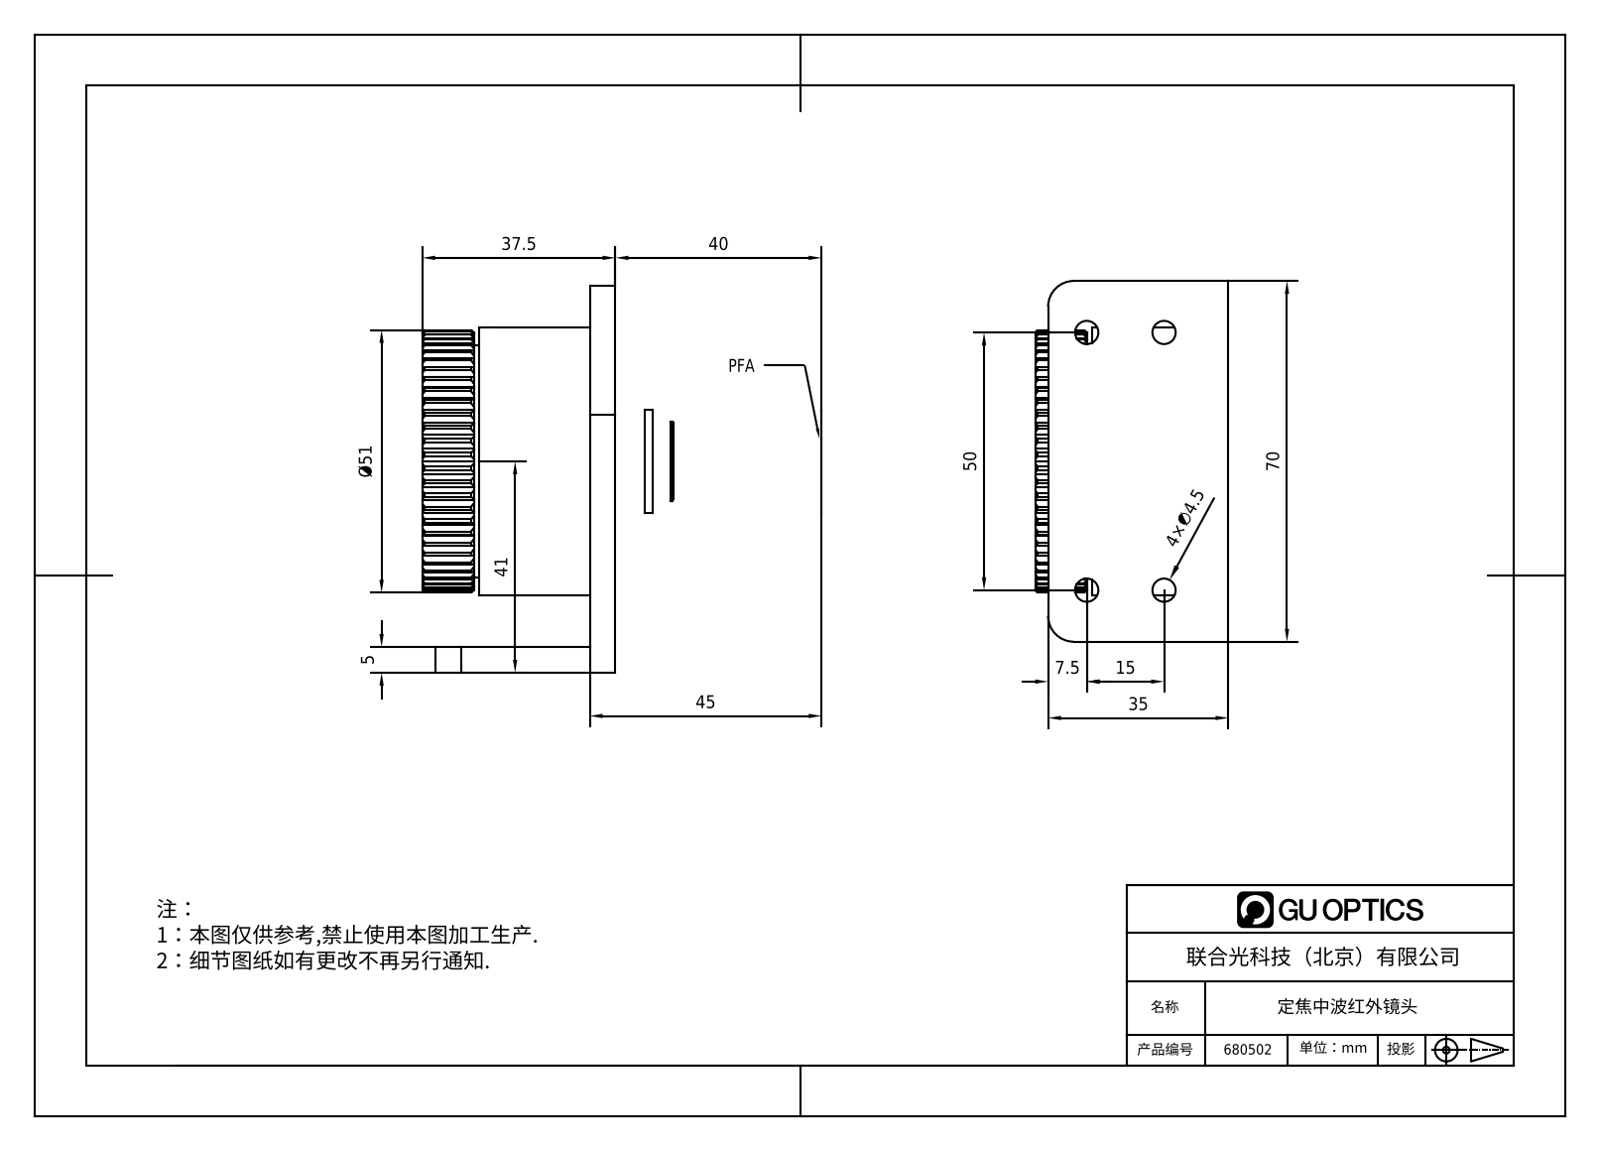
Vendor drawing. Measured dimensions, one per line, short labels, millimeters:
name: LB-0018-450F2中波制冷手动镜头外形图-20210402
written by: SolidWorks 2020 (CONFIG_CONTROL_DESIGN)
unit: mm
bodies: 17 solids, 435 faces (182 planar, 117 cylindrical, 136 other)
size: 77.51 × 75 × 70
volume: 75 246 mm³; area: 57 528 mm²
holes: 4× ⌀4.5, 1× ⌀2.05, 1× ⌀29.6, 1× ⌀31.2, 1× ⌀33, 1× ⌀34.6, 1× ⌀35.3, 1× ⌀36.3, 1× ⌀36.5, 1× ⌀38, 1× ⌀39.3, 1× ⌀40.3
bosses: 1× ⌀52, 1× ⌀50, 1× ⌀48.6, 1× ⌀46.2, 1× ⌀46, 1× ⌀44.6, 1× ⌀43.9, 1× ⌀43.6
rounds: 2× R5, 2× R25, 1× R25.5
face distances: 5, 13.5, 3.94, 1.06, 32.79, 34.66, 34.64, 70, 20.59, 24.53
hole spacings: 15, 25.24, 27.52, 50, 52.2
